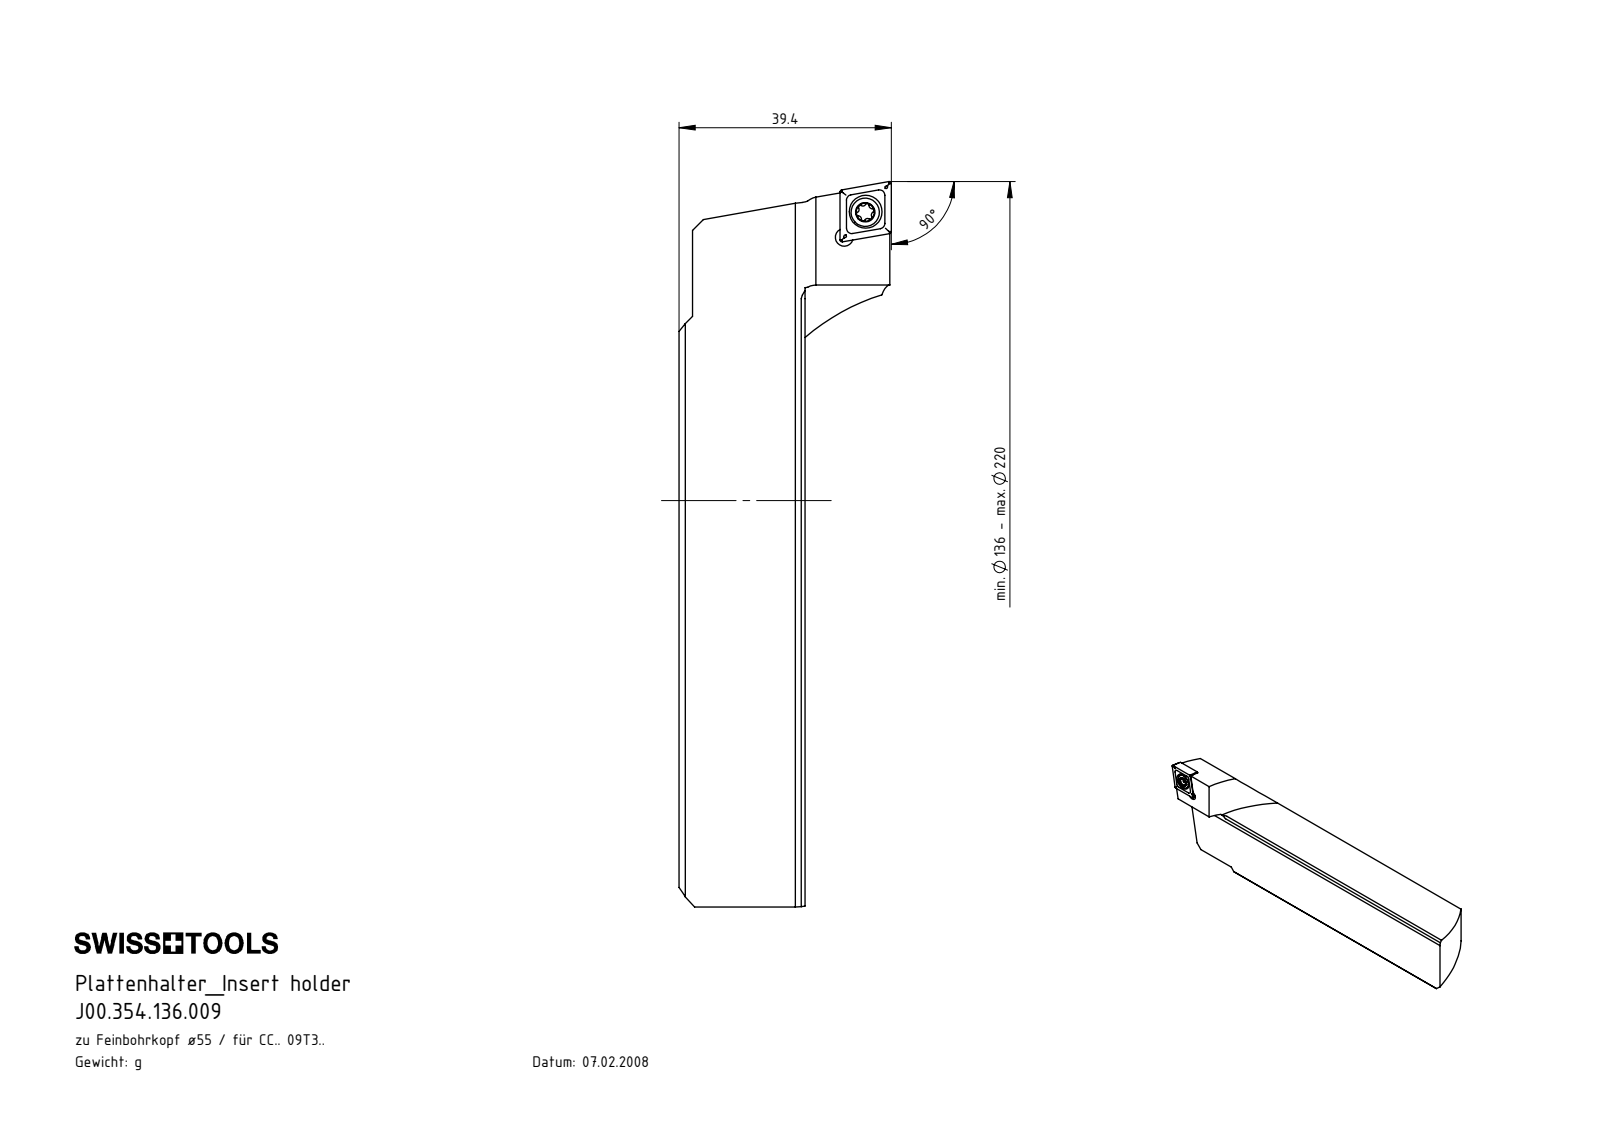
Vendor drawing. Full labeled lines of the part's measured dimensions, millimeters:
Part name (STEP PRODUCT): F00-WCB.136.001_C; WCB-ER2.001.009_A; CCMT09T304; J00.354.136.009
STEP written by: SolidWorks 2017 (CONFIG_CONTROL_DESIGN)
Units: millimetres
Bodies: 3 solids, 559 faces (342 planar, 39 cylindrical, 178 other)
Overall size (bounding box): 134.57 × 39.4 × 27.35
Volume: 55 658 mm³ · Surface area: 14 000 mm²
Round holes (diameter × count): ⌀3.3 ×2, ⌀4.4 ×1, ⌀6.1 ×1
Round bosses / shafts (diameter × count): ⌀5.25 ×1, ⌀4 ×1
Partial cylindrical surfaces — rounded edges, fillets, slot ends (radius × count): R0.2 ×8, R0.34 ×6, R0.59 ×6, R40 ×3, R0.8 ×1
Main face-to-face distances: 2.38, 21.3, 4.76, 7.14, 9.52, 4.77, 7.15, 9.53, 11.91, 14.29
Hole centre spacings: 6.06, 6.19
